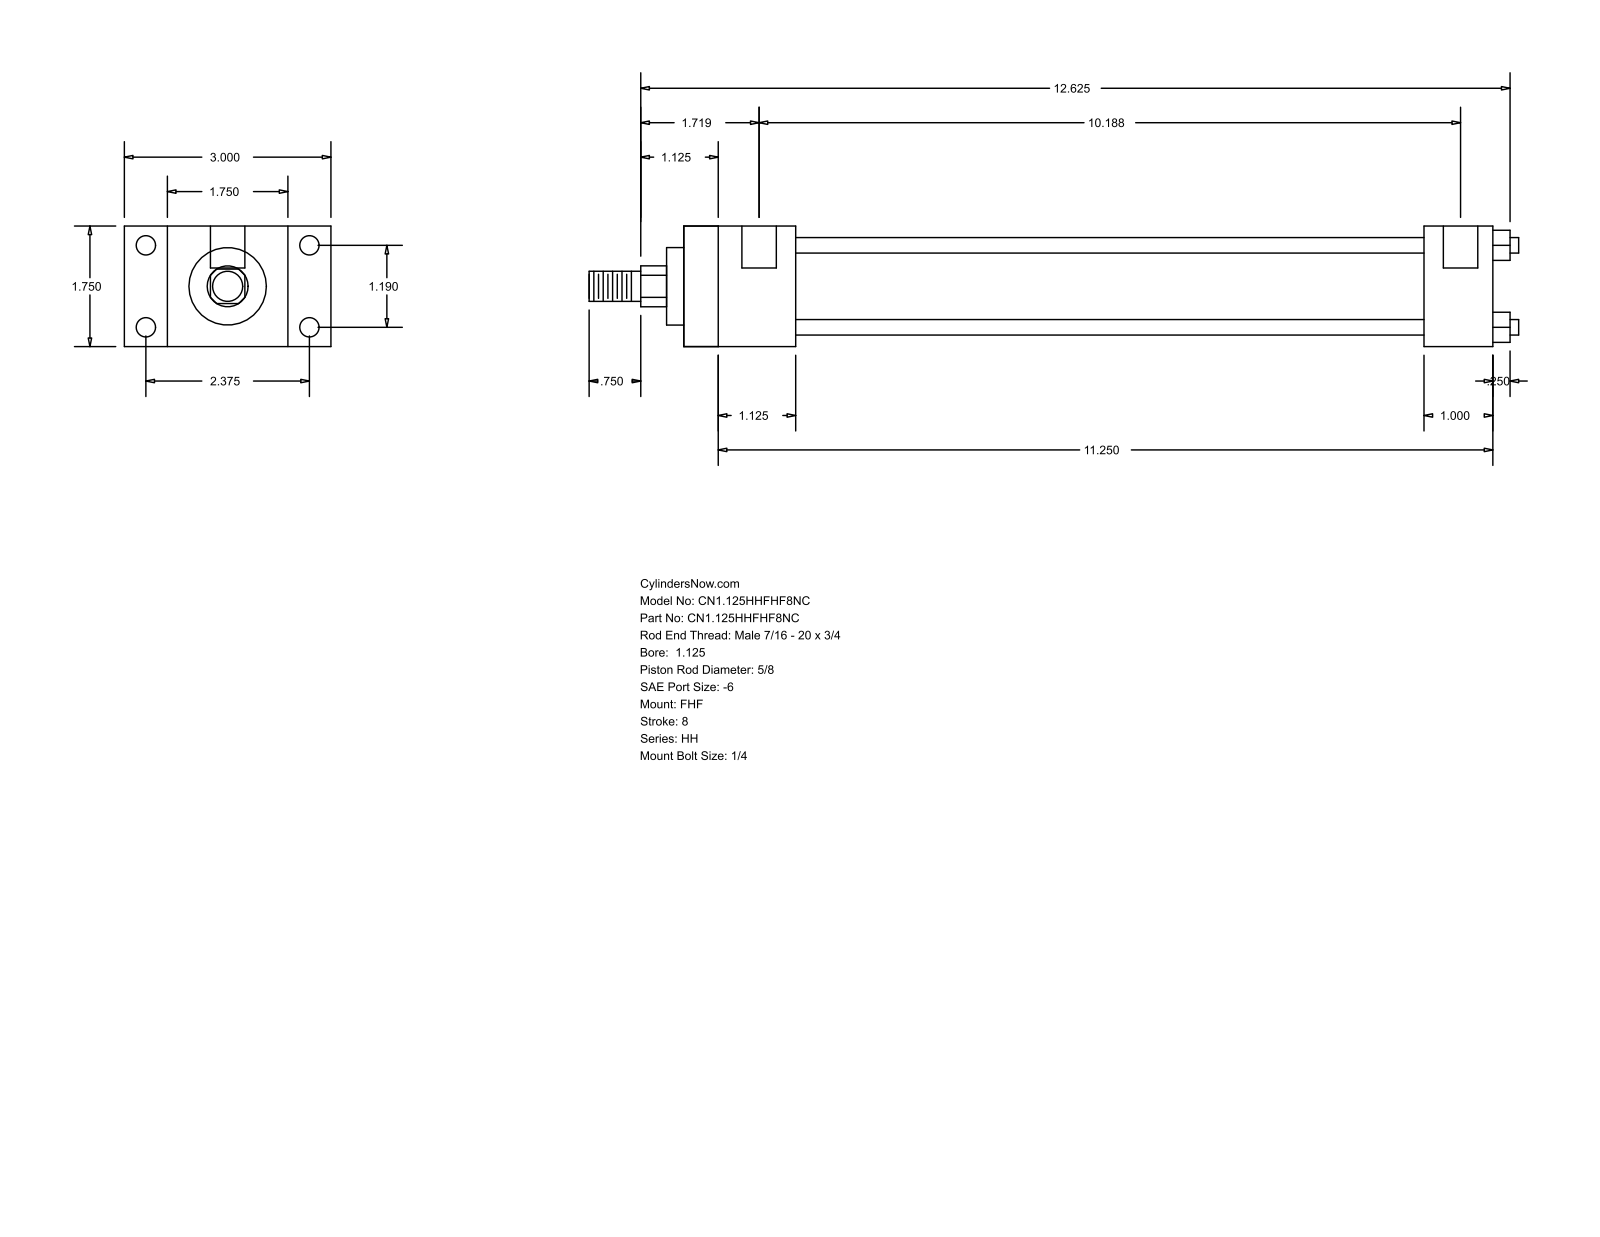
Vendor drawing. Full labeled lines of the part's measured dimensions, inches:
Part name (STEP PRODUCT): HH_FHF__0112_0.625
STEP written by: GSSL Pune (CONFIG_CONTROL_DESIGN)
Units: inches
Bodies: 0 solids, 88 faces (60 planar, 28 cylindrical, 0 other)
Overall size (bounding box): 13.5 × 3 × 1.75
Round holes (diameter × count): ⌀0.219 ×4, ⌀0.281 ×4, ⌀0.5 ×2
Round bosses / shafts (diameter × count): ⌀0.225 ×4, ⌀1.375 ×1, ⌀1.125 ×1, ⌀0.625 ×1, ⌀0.437 ×1
Partial cylindrical surfaces — rounded edges, fillets, slot ends (radius × count): R0.297 ×1
Main face-to-face distances: 1.75, 0.625, 2.375, 1.625, 3, 11.75, 10.125, 10.75, 9.125, 1
Hole centre spacings: 1.19, 2.375, 2.656, 10.063, 0.125, 10.187
